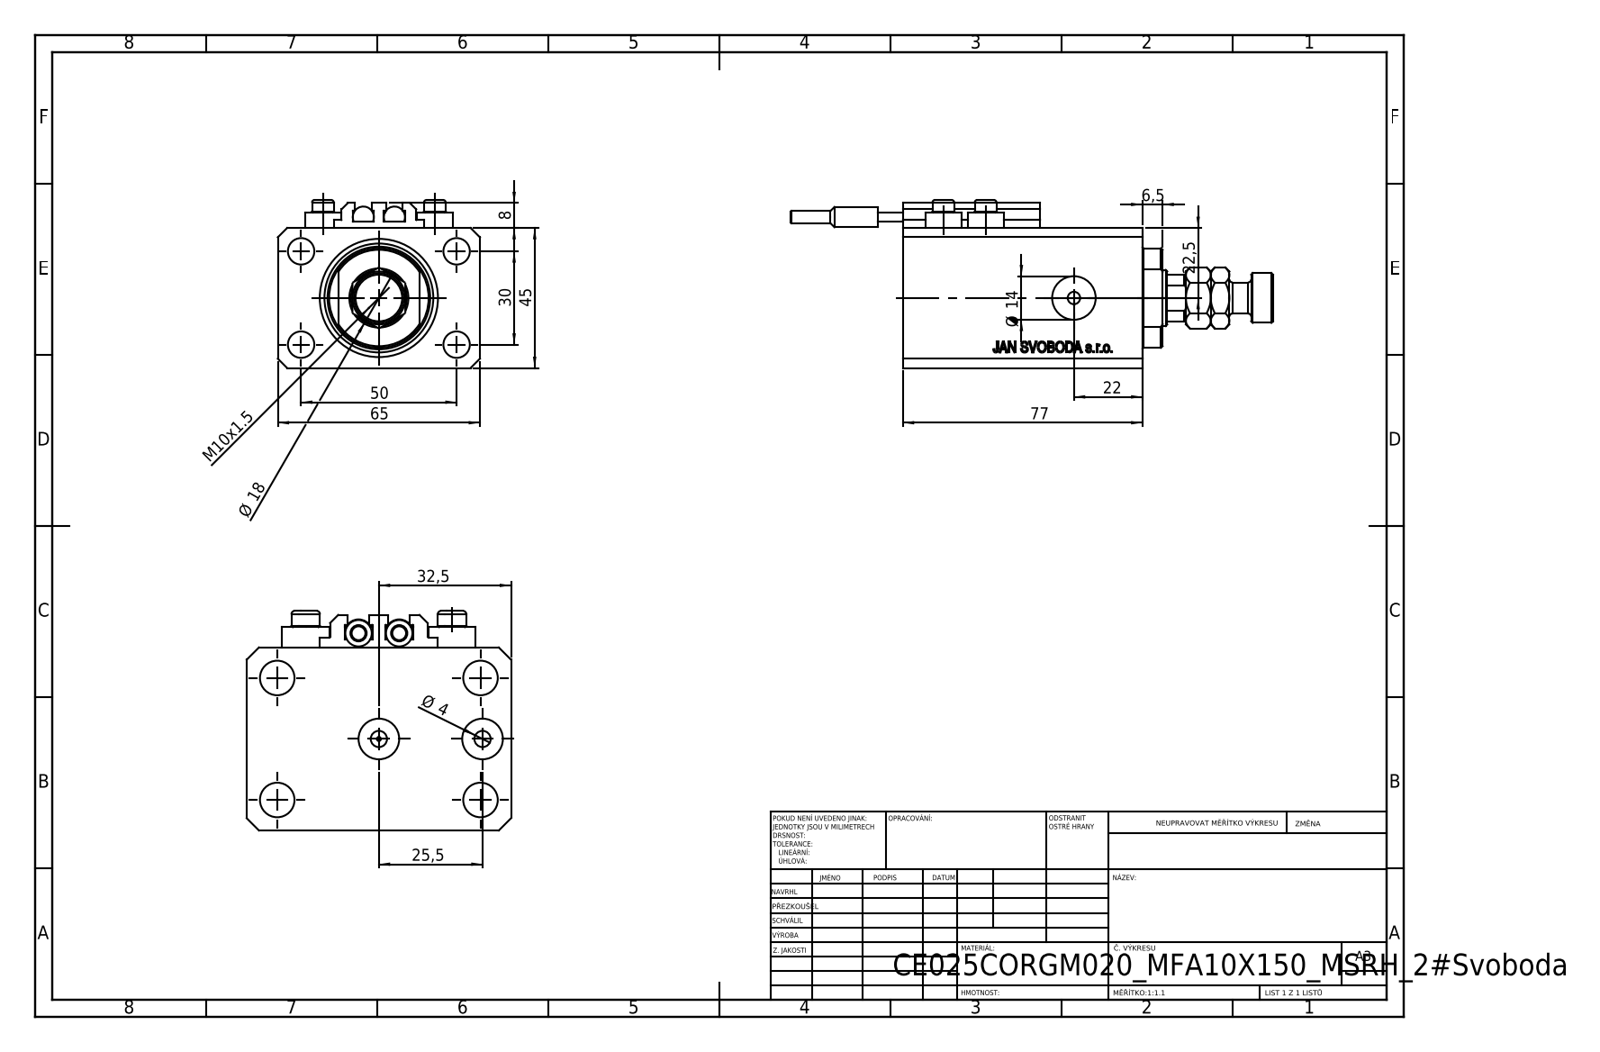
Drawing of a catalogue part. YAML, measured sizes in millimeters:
part_name: "V250CE_C_VCP; ALLEN BOLT V250CE; SWITCH_V250CE; V250CE_VC_C (+2 more)"
step_written_by: "SolidWorks 2019 (CONFIG_CONTROL_DESIGN)"
units: millimeters
bodies: {solids: 11, faces: 1146, planar: 552, cylindrical: 108, other: 486}
overall_size: [155, 65, 54]
volume: 220500
surface_area: 62495
round_holes:
  - {diameter: 4, count: 8}
  - {diameter: 8.5, count: 5}
  - {diameter: 10, count: 2}
  - {diameter: 14, count: 2}
  - {diameter: 1.25, count: 1}
  - {diameter: 18, count: 1}
  - {diameter: 25, count: 1}
  - {diameter: 38, count: 1}
round_bosses_or_shafts:
  - {diameter: 11.6, count: 4}
  - {diameter: 7, count: 4}
  - {diameter: 6.8, count: 2}
  - {diameter: 6.5, count: 2}
  - {diameter: 4, count: 2}
  - {diameter: 16, count: 1}
partial_cylinders:
  - {radius: 0.2, count: 10}
  - {radius: 8.5, count: 1}
  - {radius: 16, count: 1}
face_to_face_distances: [45, 65, 14, 77, 63, 6.9, 3, 47, 56.1, 70.1]
hole_center_spacings: [29.15, 13.6, 15.01, 30, 36, 38.48, 50, 52.68]
